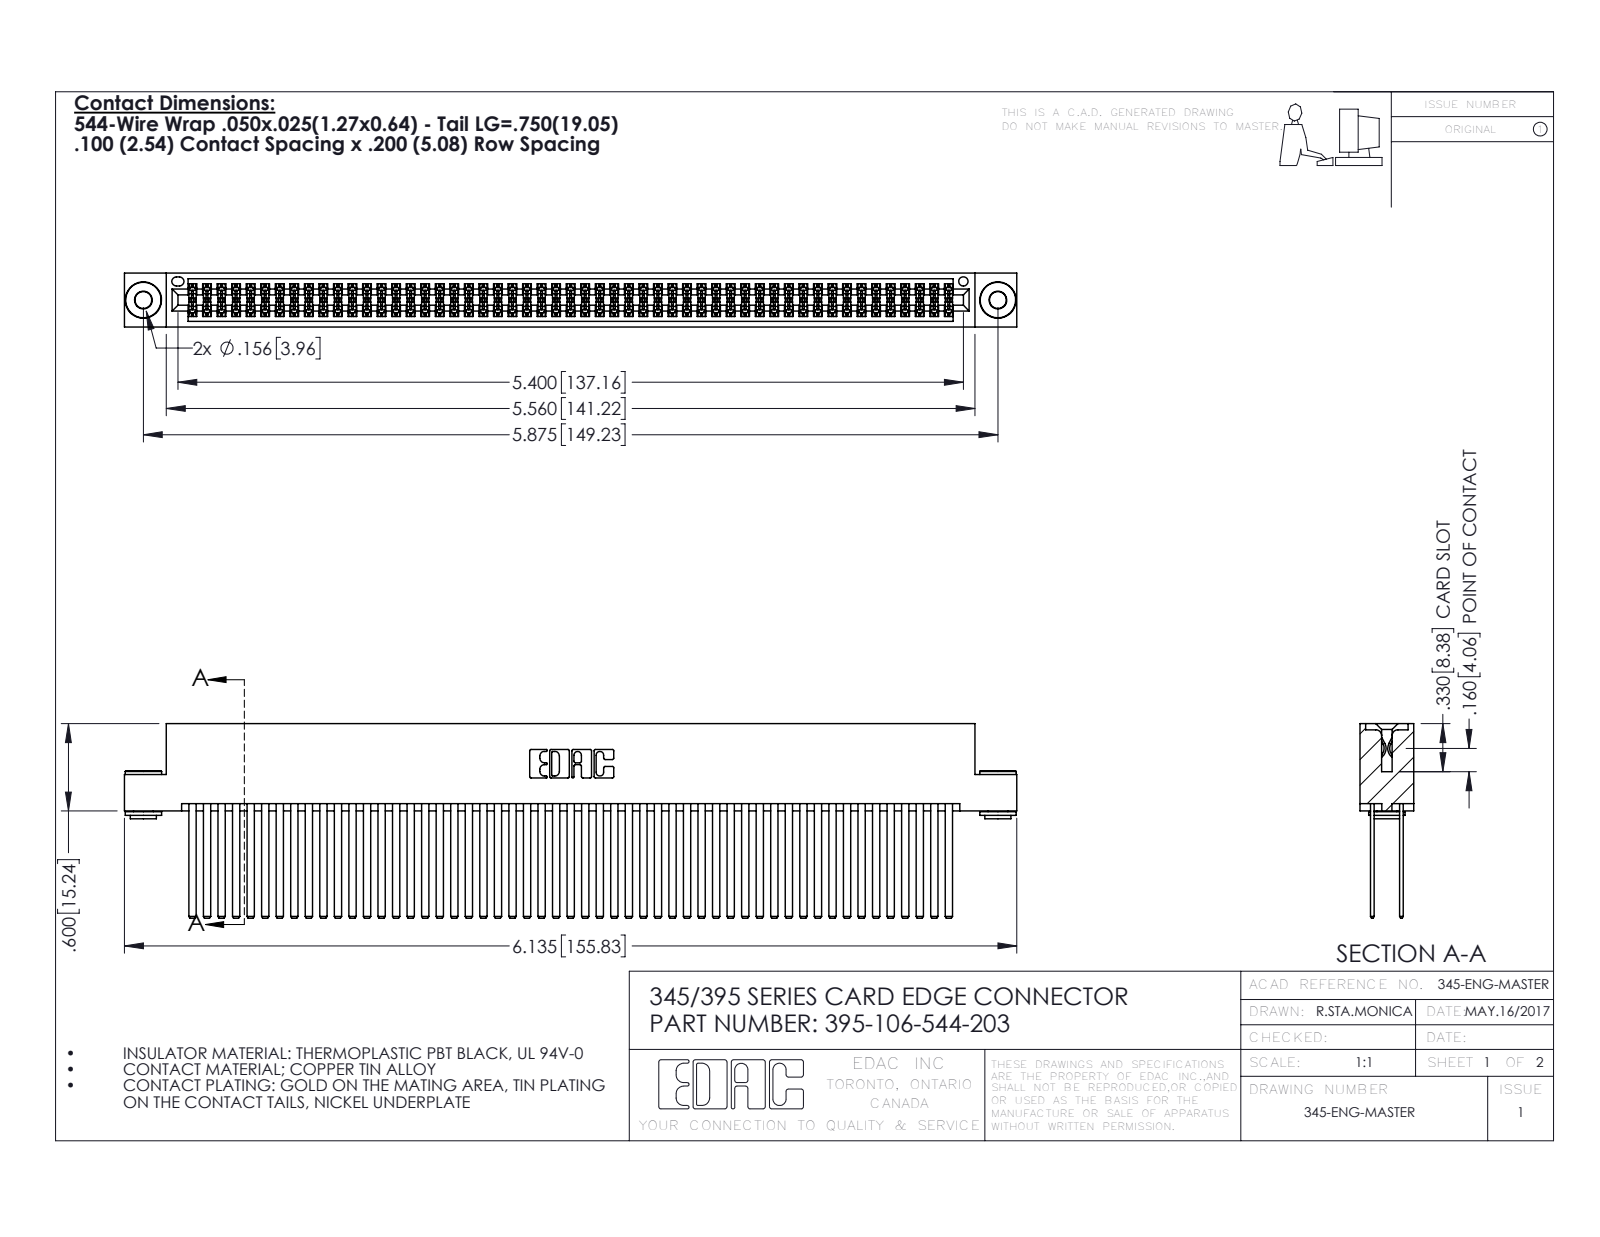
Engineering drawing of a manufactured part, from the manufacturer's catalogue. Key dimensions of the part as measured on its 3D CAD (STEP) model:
Part name (STEP PRODUCT): 345-250-002_345-250-002-102; 345 Part_Flush Mounting Lugs - 0.156 Dia-TH; 345-292-001_345-293-144; 395-106-544-203
STEP written by: SolidWorks 2016 (CONFIG_CONTROL_DESIGN)
Units: inches
Bodies: 109 solids, 4828 faces (3164 planar, 1656 cylindrical, 8 other)
Overall size (bounding box): 6.135 × 1.337 × 0.37
Volume: 1.022 in³ · Surface area: 45.76 in²
Round holes (diameter × count): ⌀0.116 ×2, ⌀0.156 ×2, ⌀0.064 ×1
Round bosses / shafts (diameter × count): ⌀0.25 ×2, ⌀0.18 ×2, ⌀0.136 ×2
Partial cylindrical surfaces — rounded edges, fillets, slot ends (radius × count): R0.006 ×159, R0.01 ×22, R0.007 ×6, R0.031 ×6, R0.026 ×3, R0.014 ×2, R0.019 ×2, R0.022 ×2
Main face-to-face distances: 0.2, 0.025, 0.072, 0.098, 0.272, 0.298, 0.225, 0.175, 0.37, 0.05
Hole centre spacings: 0.27, 5.639, 5.875
